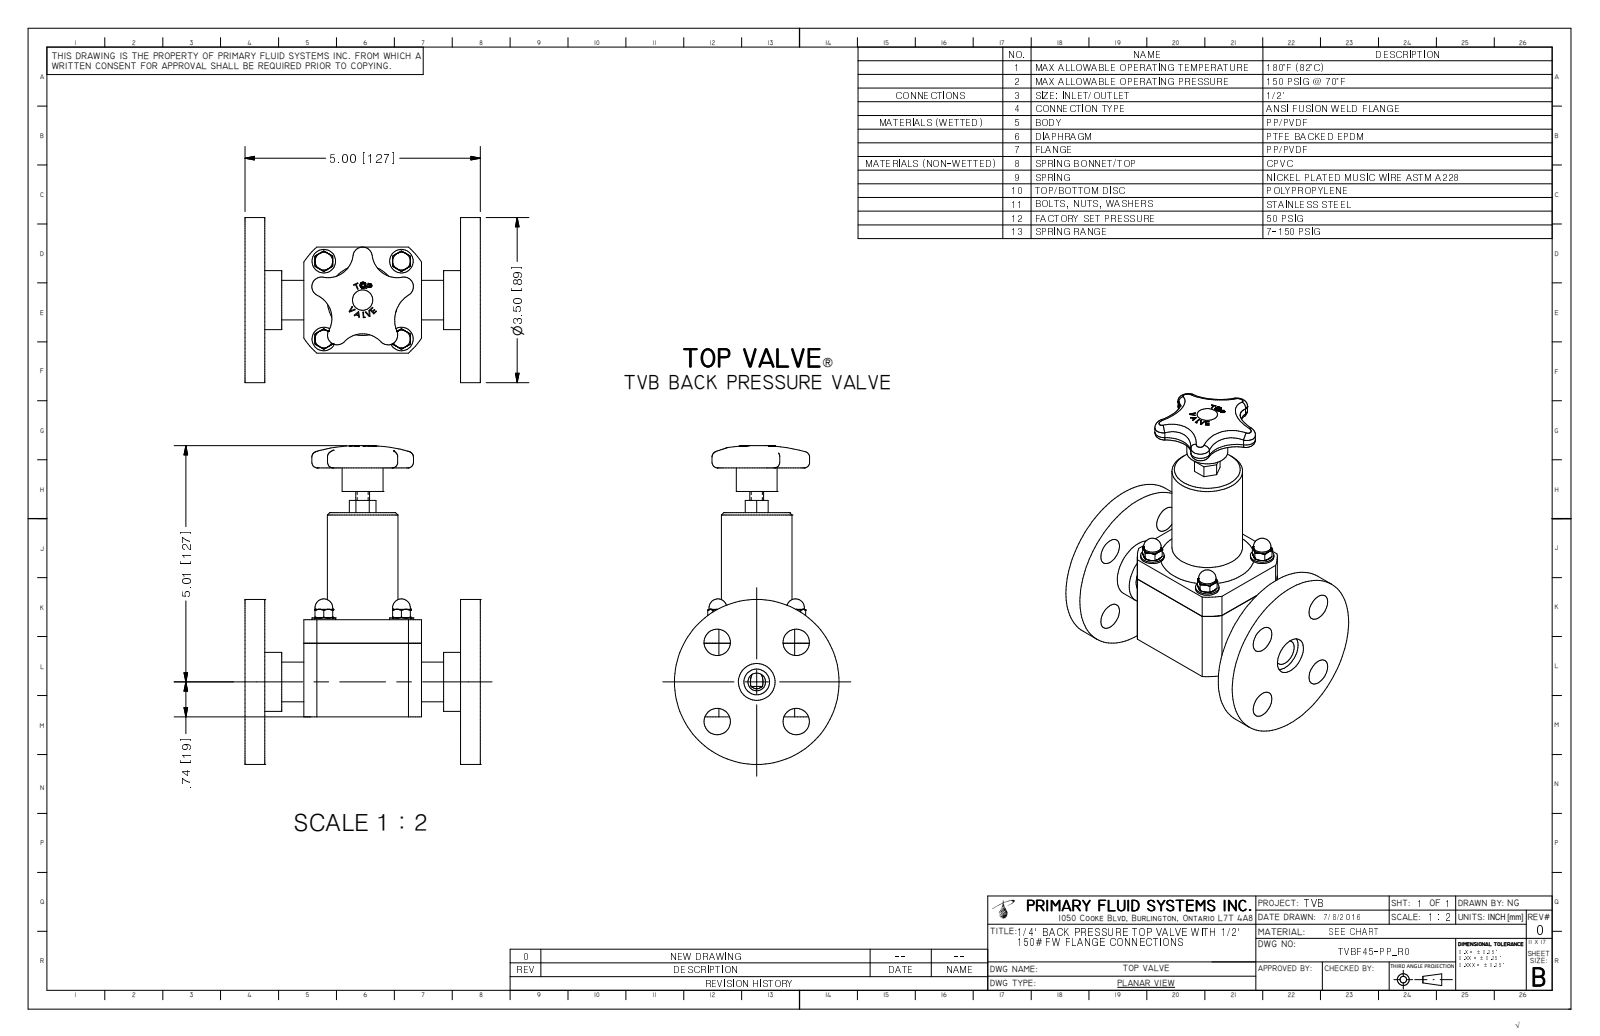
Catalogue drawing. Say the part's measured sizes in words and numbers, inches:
The part is named "TVBF45-PP_R0". Its 3-D file was written by "Autodesk Inventor 2009 (AUTOMOTIVE_DESIGN)". It is 1 solid with 361 faces: 148 planar, 61 cylindrical and 152 other. Overall it measures 6.762 by 5 by 3.5 inches. Its volume is 24.37 cubic inches and its surface area 113.3 square inches. Round holes: 4 of diameter 0.147, 4 of diameter 0.56, 1 of diameter 0.546, 1 of diameter 0.78. Round bosses or shafts: 4 of diameter 0.5, 4 of diameter 0.375, 4 of diameter 0.312, 1 of diameter 3.5, 1 of diameter 1.5, 1 of diameter 1.25, 1 of diameter 0.87, 1 of diameter 0.84. Partial cylindrical surfaces (rounded edges, fillets, slot ends): 5 of radius 0.085, 5 of radius 0.205, 4 of radius 0.536, 4 of radius 0.656, 1 of radius 0.625, 1 of radius 0.745, 1 of radius 1.488. The main face-to-face distances are 0.42, 4.58, 5, 4.16, 1.25, 3.75, 0.83, 3.33, 2.25, 2.5. The hole center spacings are 1.65, 1.187, 1.188, 1.679, 1.68, 2.333, 2.375.
